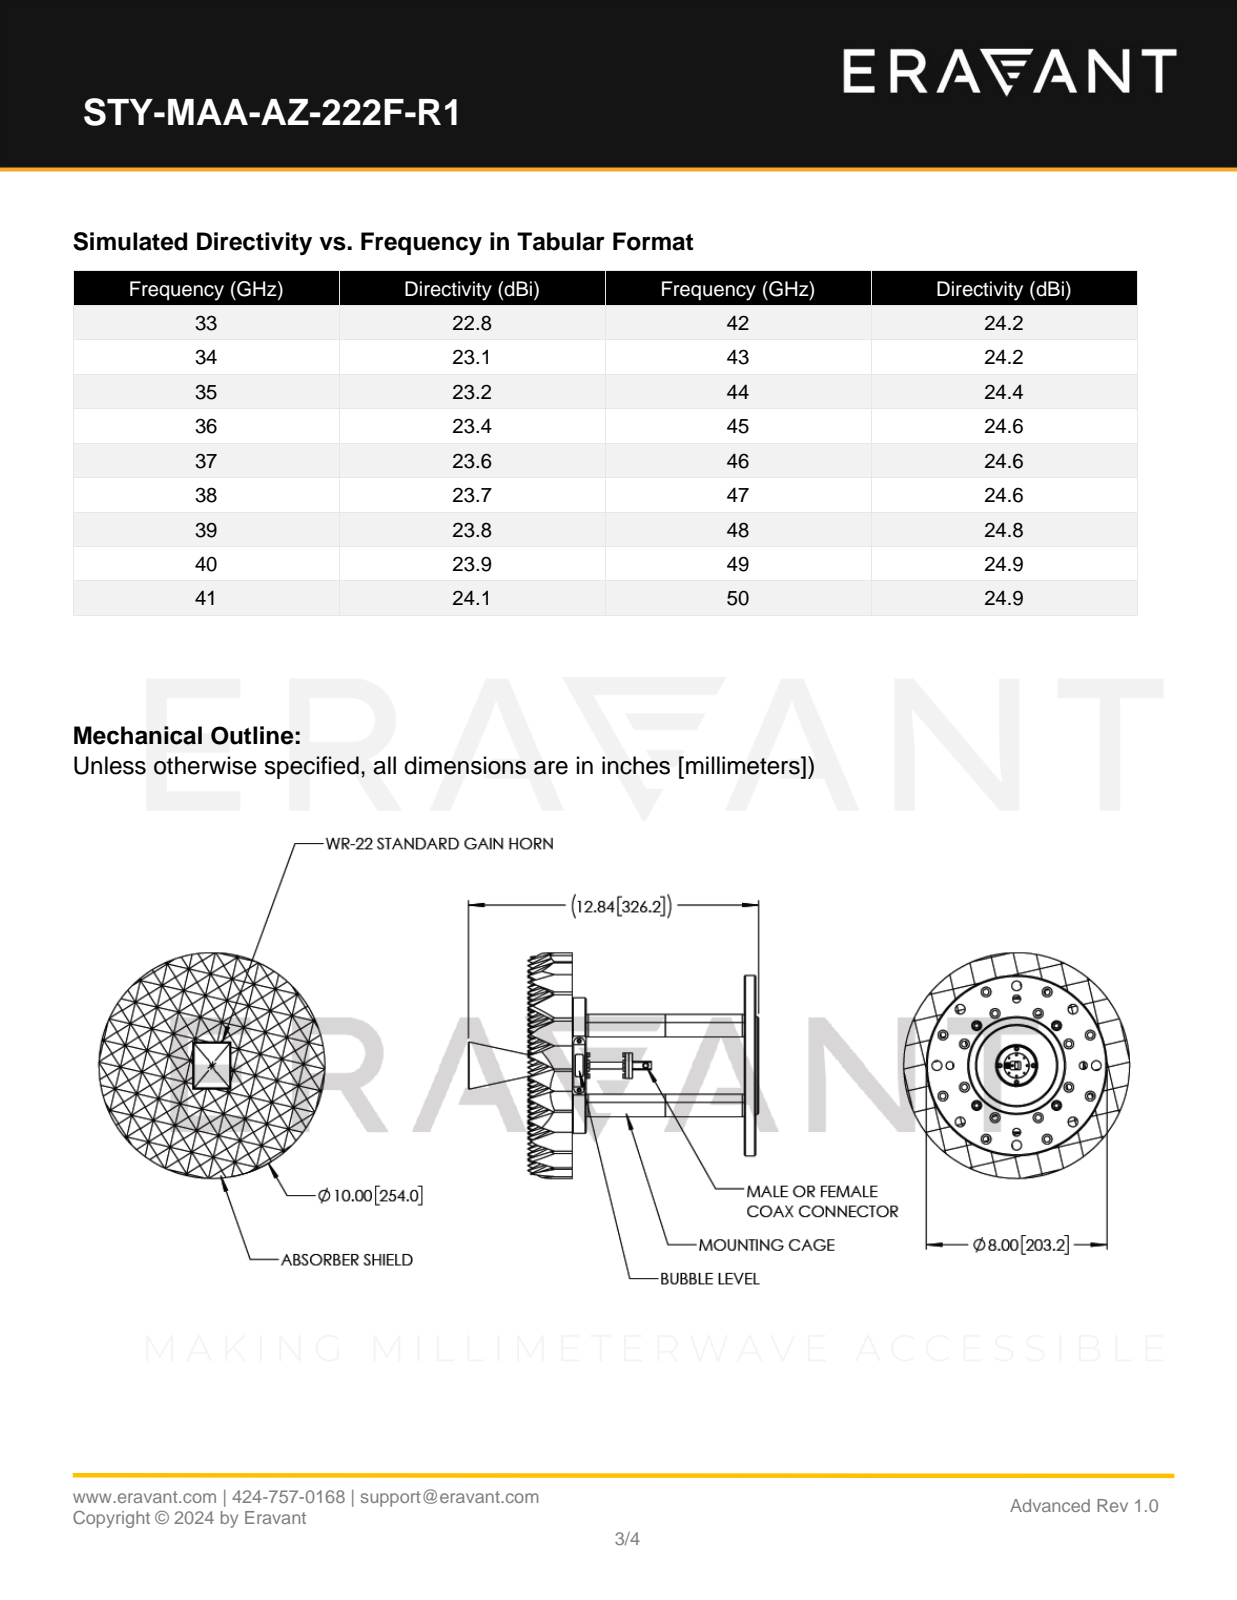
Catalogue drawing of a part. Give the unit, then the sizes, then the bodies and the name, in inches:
Units: inches
Overall size (bounding box): 12.844 × 10 × 10
Round holes (diameter × count): ⌀0.266 ×20, ⌀0.437 ×16, ⌀0.433 ×8, ⌀0.348 ×4, ⌀0.75 ×4, ⌀0.089 ×2, ⌀0.125 ×2, ⌀0.182 ×1, ⌀1.8 ×1, ⌀3.543 ×1
Round bosses / shafts (diameter × count): ⌀1 ×4, ⌀0.437 ×4, ⌀0.18 ×4, ⌀0.5 ×2, ⌀10 ×1, ⌀8 ×1, ⌀6 ×1, ⌀4.331 ×1
Partial cylindrical surfaces — rounded edges, fillets, slot ends (radius × count): R0.005 ×48, R0.08 ×2, R0.25 ×2, R0.24 ×1
Main face-to-face distances: 0.984, 1.969, 0.985, 1.969, 2.953, 3.938, 3.937, 5.906, 2.953, 4.922
Hole centre spacings: 4.326, 5.585, 3.458, 5.046, 5.918, 1.551, 2.496, 3.53
Volume: 157 in³ · Surface area: 779.8 in²
Bodies: 83 solids, 1422 faces (616 planar, 339 cylindrical, 467 other)
Part name (STEP PRODUCT): STY-MAA-AZ-222F-R1
STEP written by: SolidWorks 2021 (CONFIG_CONTROL_DESIGN)
